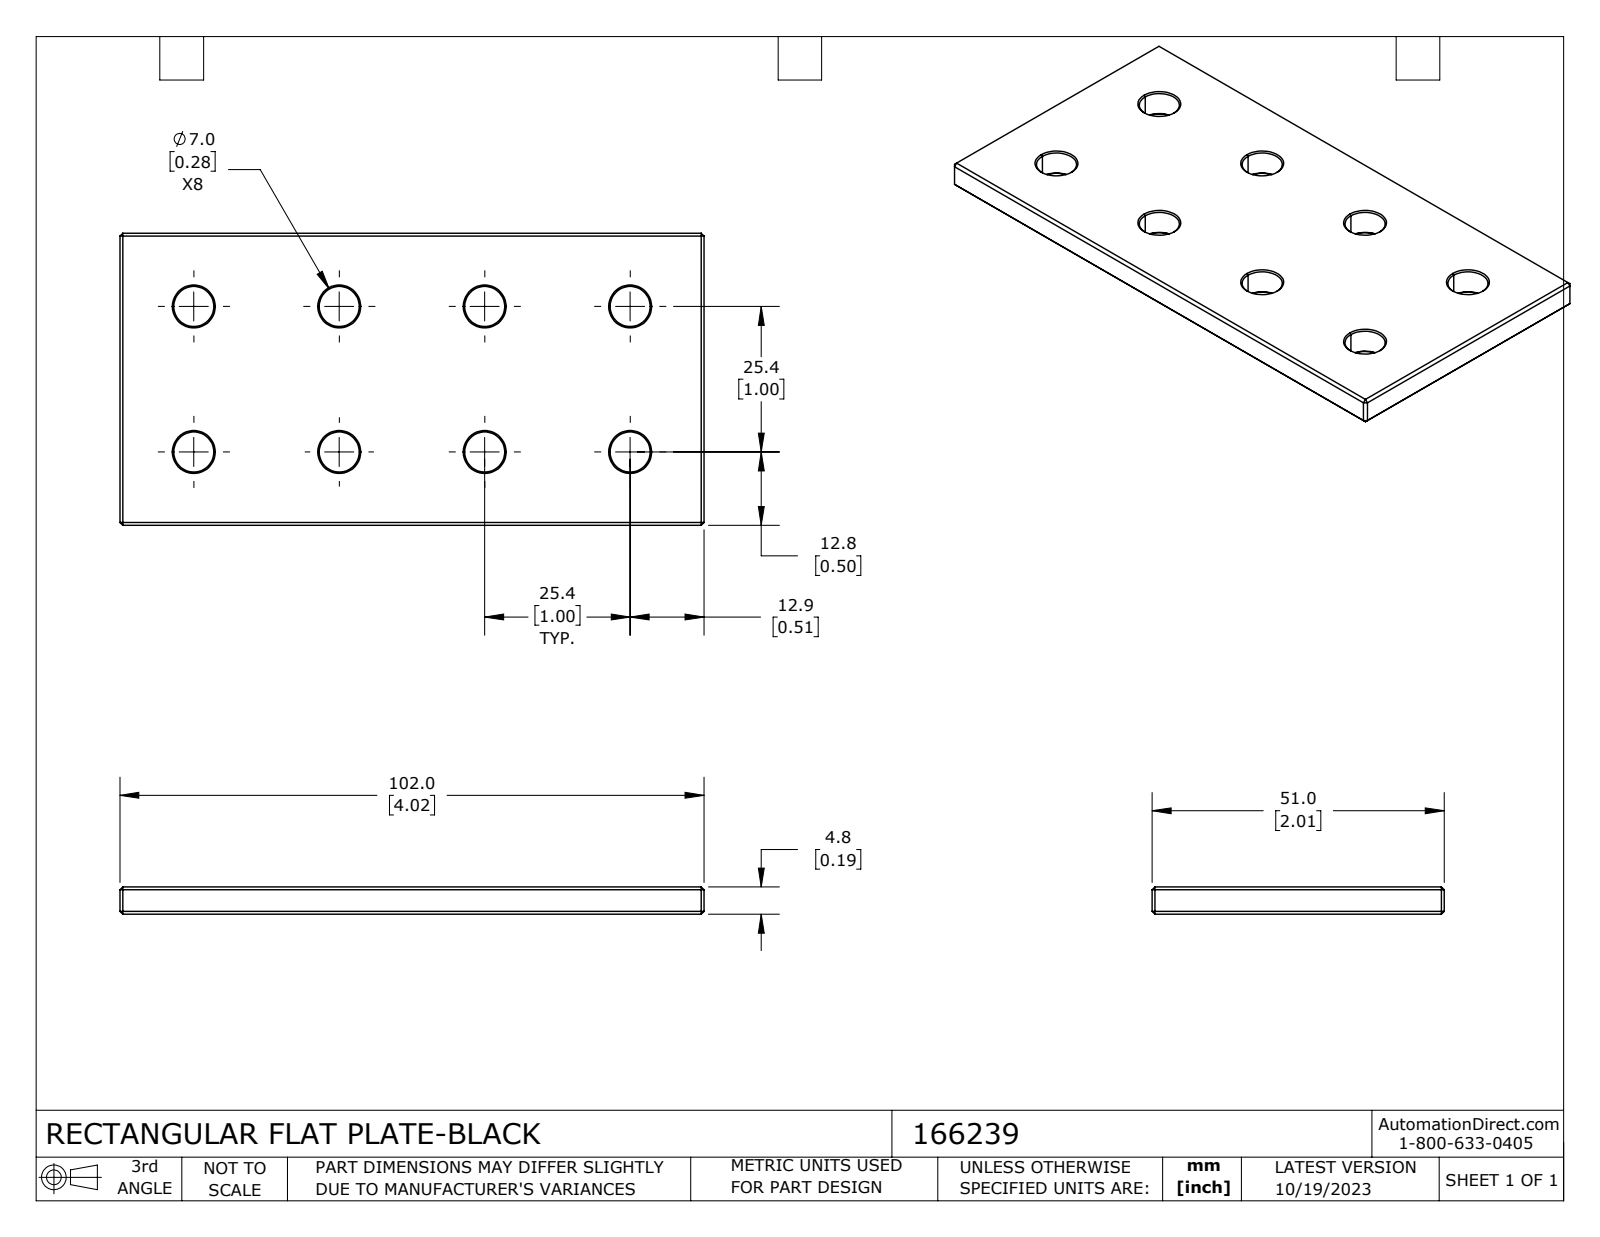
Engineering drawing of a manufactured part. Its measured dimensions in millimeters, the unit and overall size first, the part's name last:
Units: millimetres
Overall size (bounding box): 102 × 51 × 4.76
Round holes (diameter × count): ⌀7 ×8
Main face-to-face distances: 4.76, 51, 102, 38.72, 74.77, 107.46, 89.87
Hole centre spacings: 25.4, 35.92, 50.8, 56.8, 76.2, 80.32
Volume: 23 219 mm³ · Surface area: 11 848 mm²
Bodies: 1 solid, 74 faces (26 planar, 16 cylindrical, 32 other)
Part name (STEP PRODUCT): 166239
STEP written by: SolidWorks 2023 (CONFIG_CONTROL_DESIGN)
